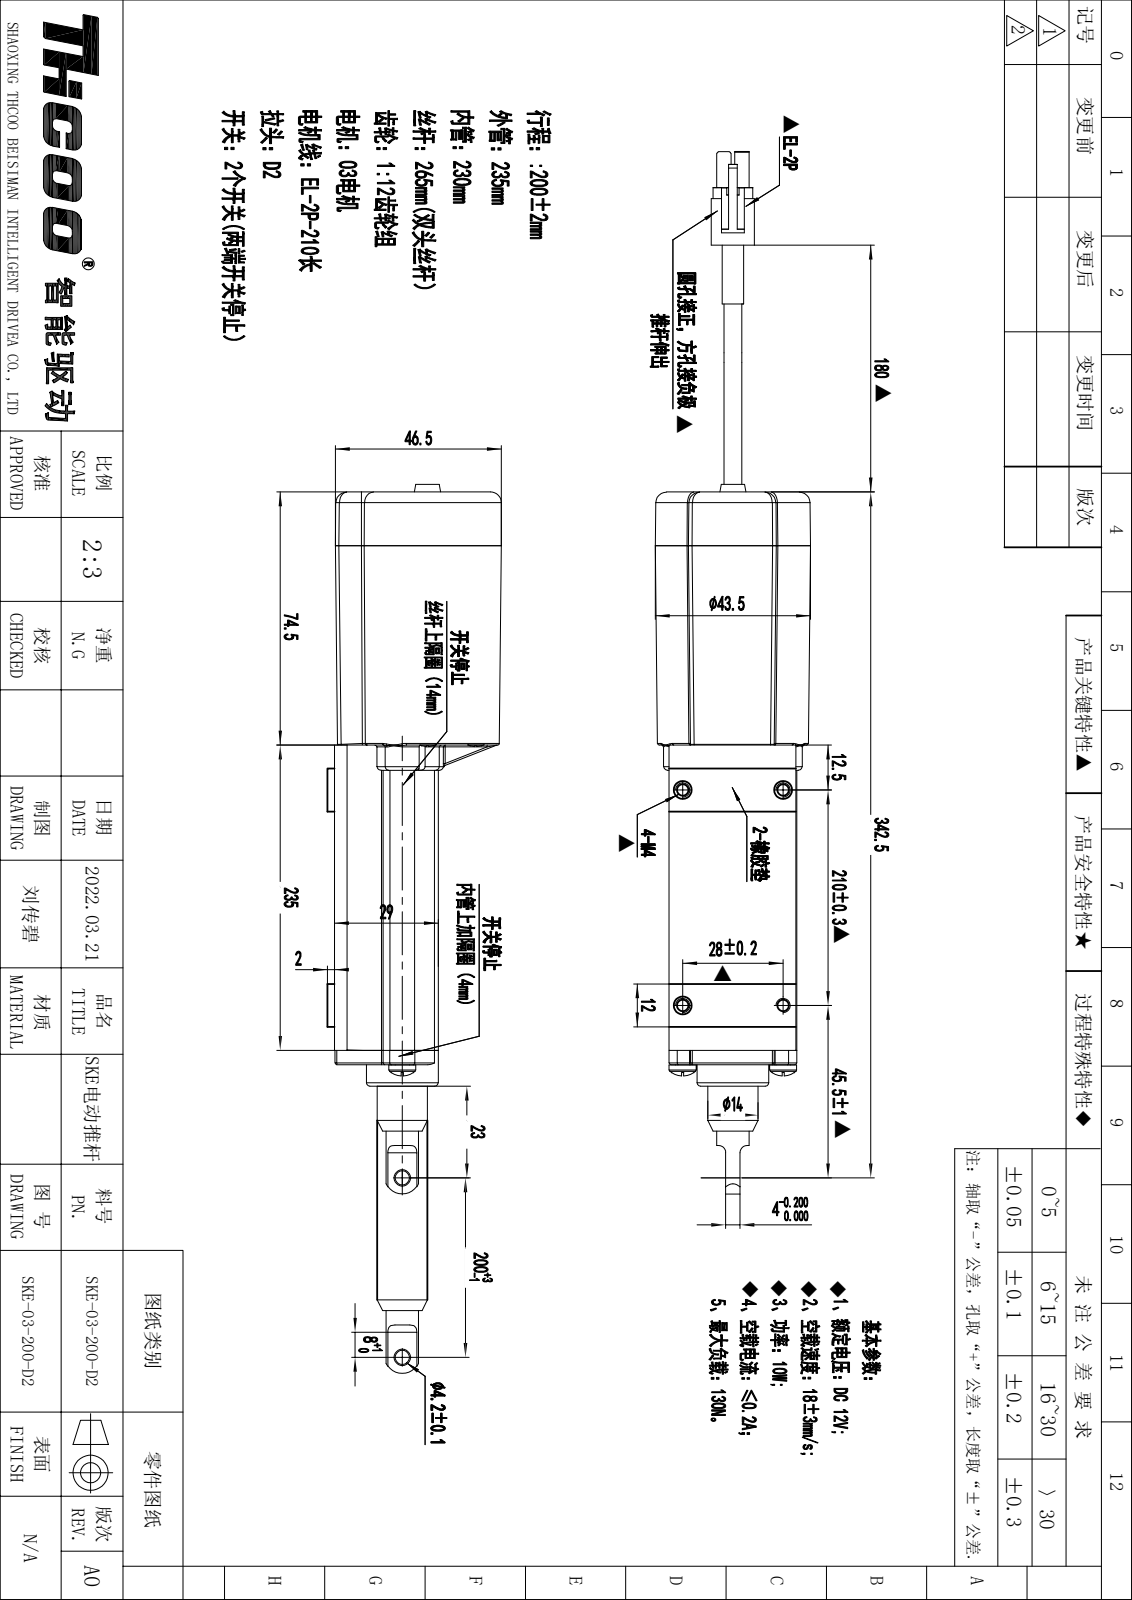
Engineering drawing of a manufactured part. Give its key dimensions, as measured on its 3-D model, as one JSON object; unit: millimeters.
{"part_name": "Admi0CB42C5Fkiey", "step_written_by": "SIEMENS PLM Software NX 12.0 (AUTOMOTIVE_DESIGN)", "units": "millimeters", "bodies": {"solids": 8, "faces": 773, "planar": 321, "cylindrical": 248, "other": 204}, "overall_size": [420.13, 48.47, 43.25], "volume_mm3": 158719, "surface_area_mm2": 141246, "round_holes": [[4, 4], [4.8, 4], [3.2, 3], [4.2, 3], [5, 3], [6.3, 1], [7, 1], [8.2, 1], [10, 1], [14.2, 1], [16, 1]], "round_bosses_or_shafts": [[7.5, 2], [4, 2], [20, 1], [15.9, 1], [15, 1], [14, 1], [12, 1], [9, 1]], "partial_cylinders_radius": [[0.5, 97], [1, 19], [0.2, 8], [0.4, 7], [2, 6], [3, 6], [1.08, 4], [1.8, 4]], "face_to_face_distances": [2, 21.3, 1.5, 3.5, 23.3, 6, 2.5, 8, 8.85, 6.85], "hole_center_spacings": [28, 7.16, 14, 17.01, 30.32, 220, 221.77, 15.51]}
